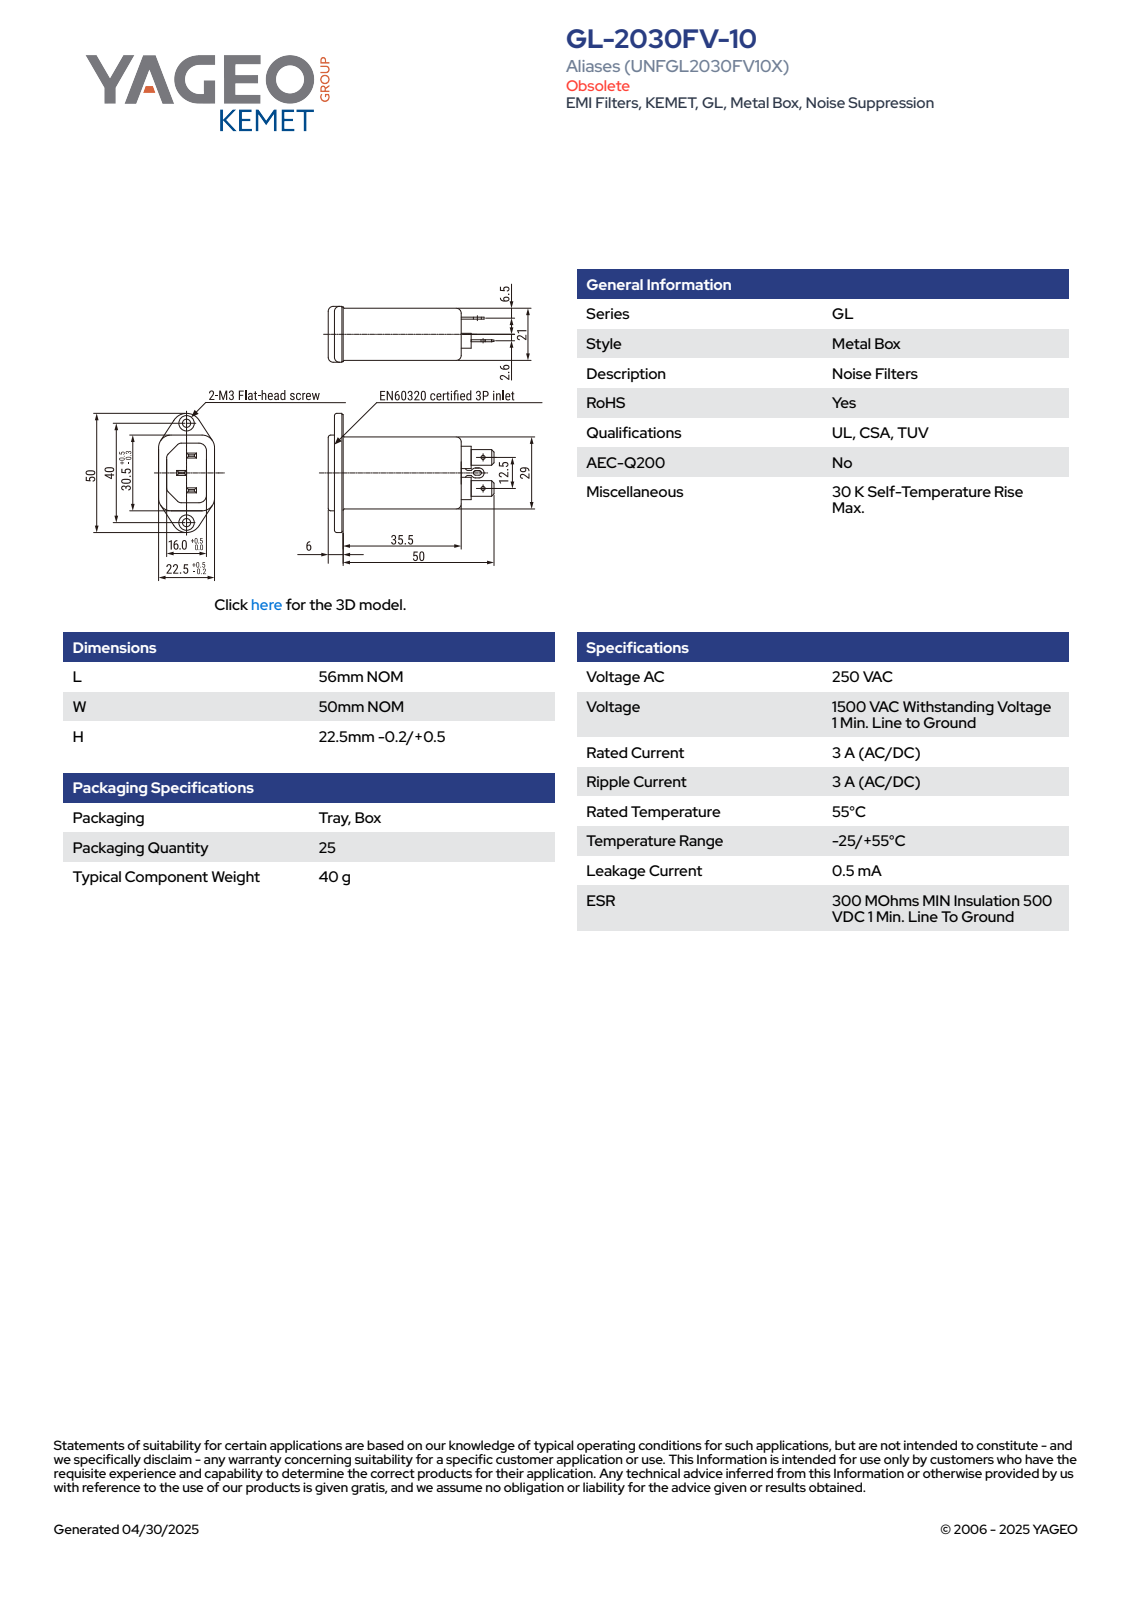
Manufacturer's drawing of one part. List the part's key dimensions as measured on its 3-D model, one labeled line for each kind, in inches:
Part name (STEP PRODUCT): ENF_KGLFVP_L56W50H23
STEP written by: SolidWorks 2014 (AUTOMOTIVE_DESIGN)
Units: inches
Bodies: 1 solid, 192 faces (99 planar, 61 cylindrical, 32 other)
Overall size (bounding box): 2.441 × 1.969 × 0.906
Volume: 1.841 in³ · Surface area: 11.57 in²
Round holes (diameter × count): ⌀0.118 ×2
Round bosses / shafts (diameter × count): ⌀0.031 ×6, ⌀0.205 ×2
Partial cylindrical surfaces — rounded edges, fillets, slot ends (radius × count): R0.039 ×22, R0.079 ×12, R0.118 ×2, R0.044 ×1
Main face-to-face distances: 0.866, 1.142, 1.76, 0.079, 0.039, 1.681, 0.827, 0.108, 0.758, 0.069
Hole centre spacings: 1.575
